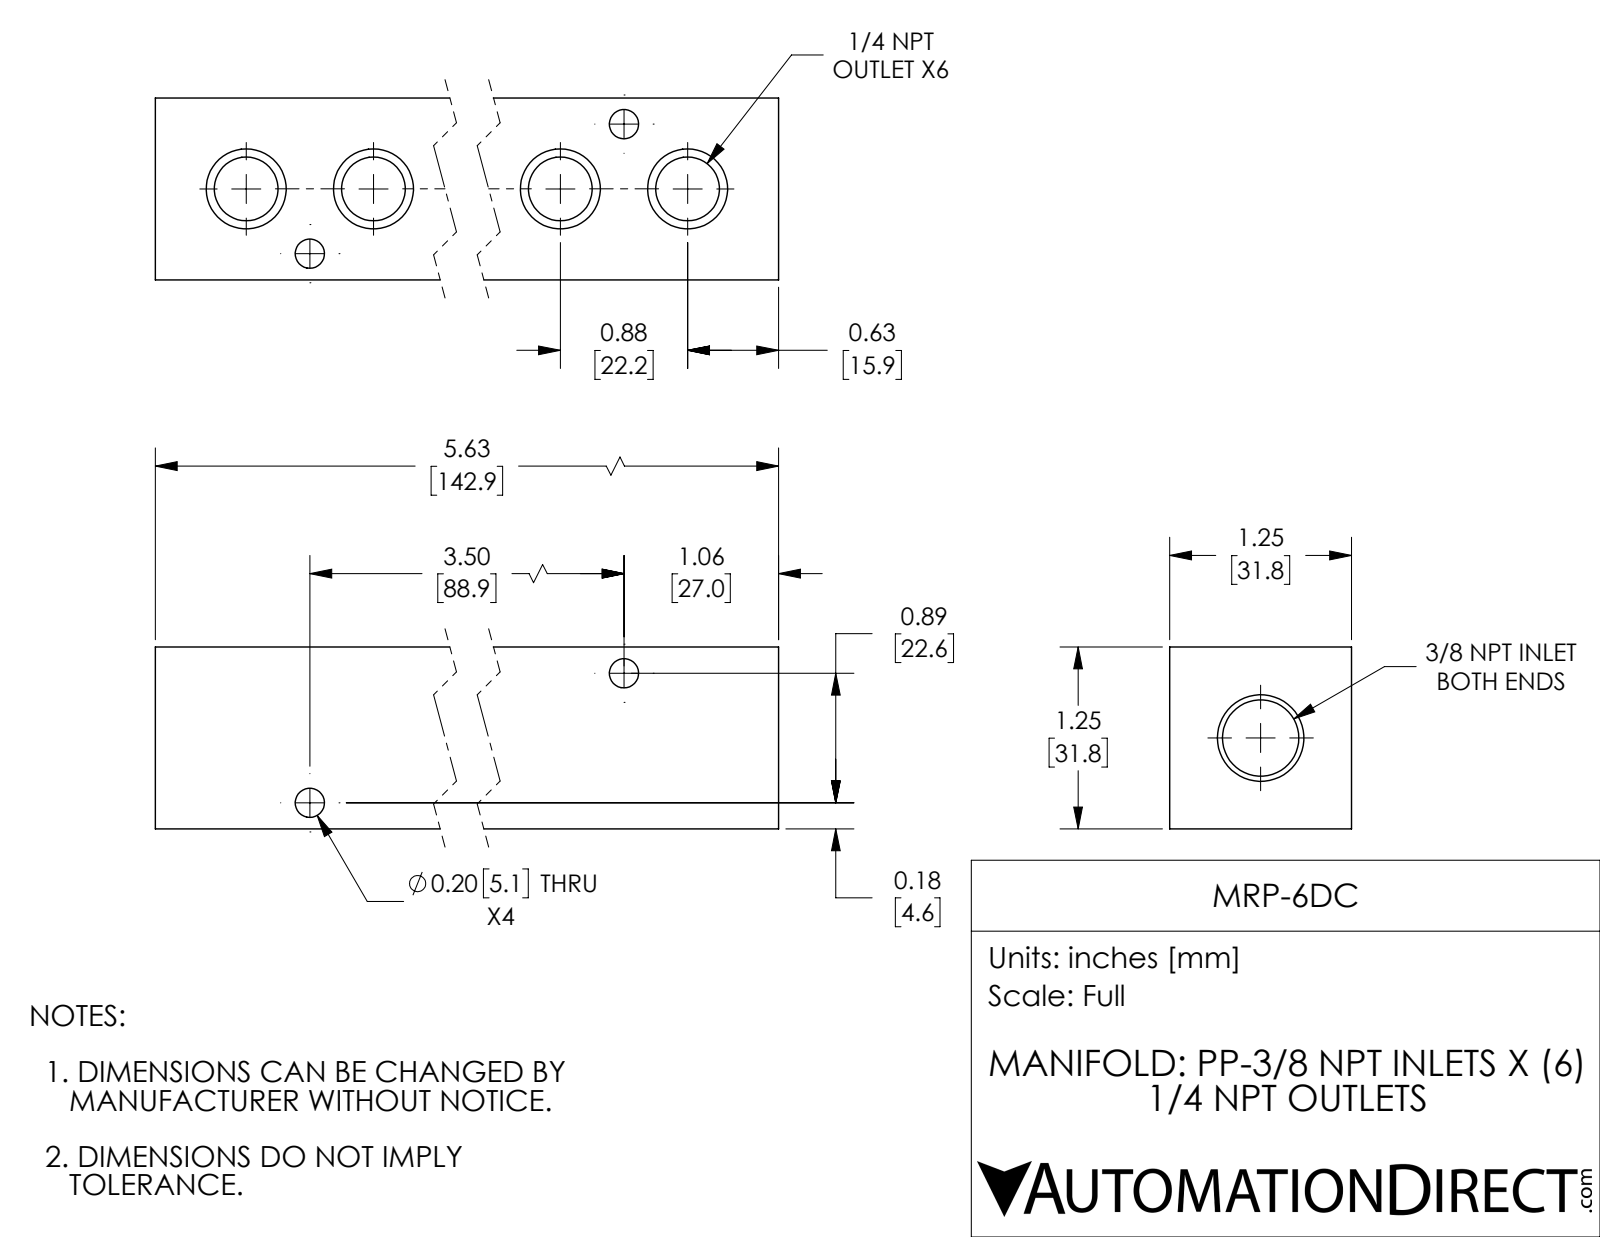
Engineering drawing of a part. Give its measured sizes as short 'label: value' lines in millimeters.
name: MRP-6DC
written by: SolidWorks 2018 (AUTOMOTIVE_DESIGN)
unit: mm
bodies: 1 solid, 52 faces (6 planar, 30 cylindrical, 16 other)
size: 142.9 × 31.8 × 31.8
volume: 115 600 mm³; area: 28 320 mm²
holes: 6× ⌀11.1, 4× ⌀5.1, 1× ⌀13.3
face distances: 31.8, 142.9
hole spacings: 15.8, 22.2, 44.5, 22.2, 66.7, 91.7, 100.7, 35.2
